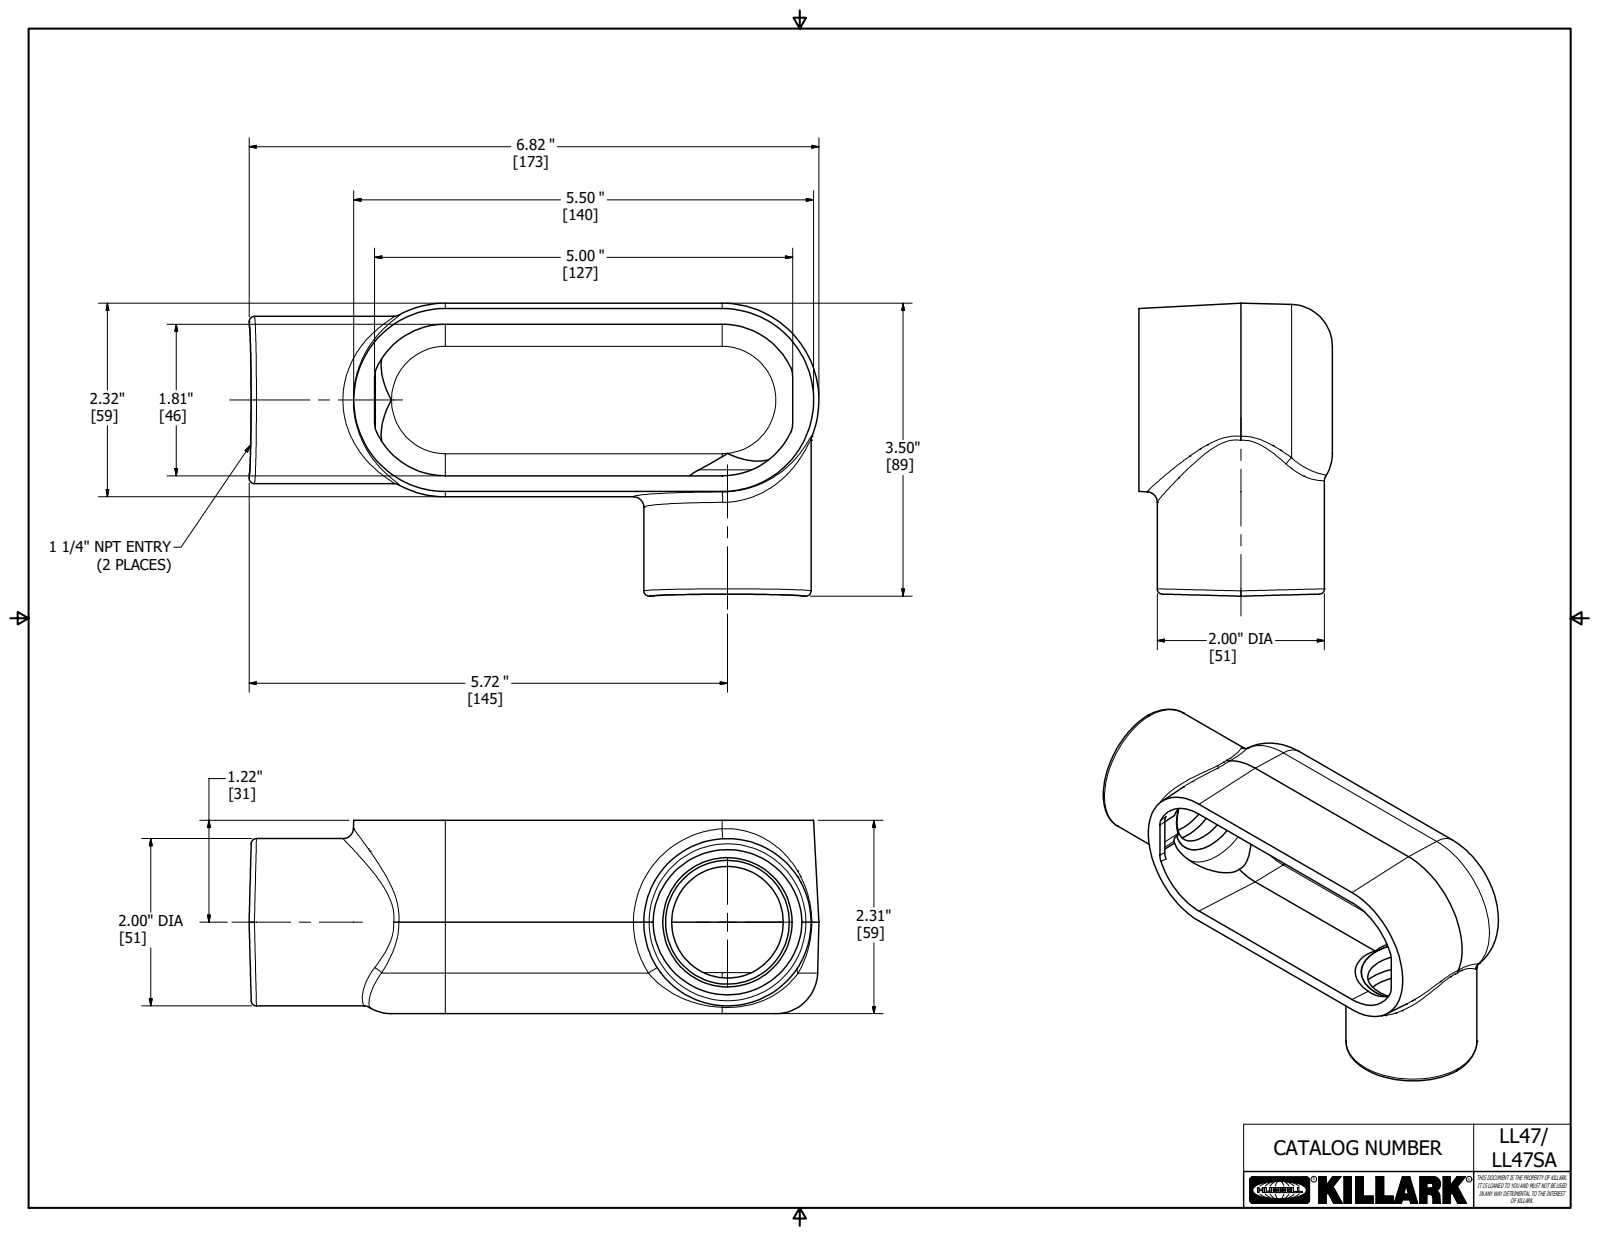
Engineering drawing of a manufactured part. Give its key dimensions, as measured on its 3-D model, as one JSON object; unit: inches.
{"part_name": "17683_e", "step_written_by": "Autodesk Inventor 2018 (AUTOMOTIVE_DESIGN)", "units": "inches", "bodies": {"solids": 1, "faces": 102, "planar": 36, "cylindrical": 18, "other": 48}, "overall_size": [6.815, 3.503, 2.312], "volume_in3": 9.375, "surface_area_in2": 102.8, "round_holes": [[1.666, 2], [1.813, 1]], "round_bosses_or_shafts": [[2, 2]], "partial_cylinders_radius": [[0.05, 4], [0.125, 4], [0.313, 2], [0.5, 2], [0.906, 1]], "face_to_face_distances": [0.187, 0.188, 2.312, 2.125, 0.031, 0.156, 2.281, 1.187, 1.375, 3.315]}
